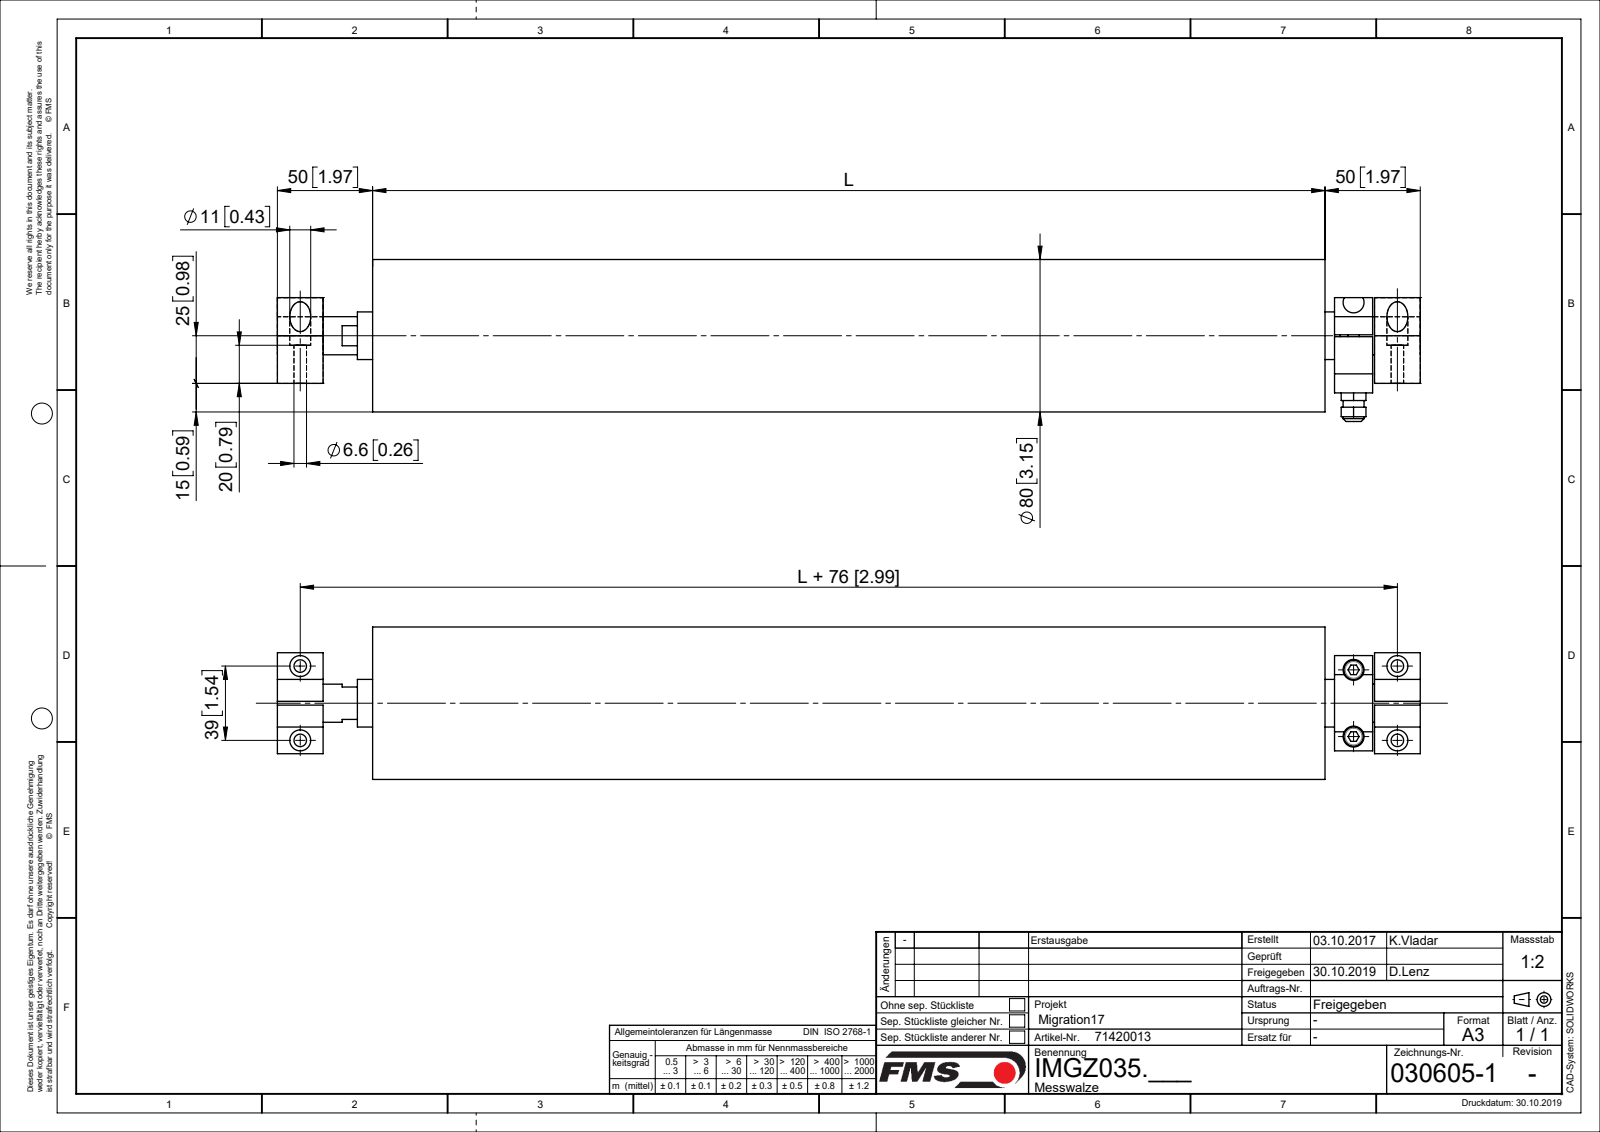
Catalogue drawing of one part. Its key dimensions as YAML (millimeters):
part_name: "I0306051_800; I0306052; PENDELKUGELLAGER_1207; I0306053 (+8 more)"
step_written_by: "Mechanical Desktop 2007 (CONFIG_CONTROL_DESIGN)"
units: millimeters
bodies: {solids: 23, faces: 548, planar: 218, cylindrical: 230, other: 100}
overall_size: [900, 86, 80]
volume: 2535000
surface_area: 606645
round_holes:
  - {diameter: 11, count: 6}
  - {diameter: 6.4, count: 4}
  - {diameter: 6.6, count: 4}
  - {diameter: 5, count: 2}
  - {diameter: 5.15, count: 2}
  - {diameter: 7, count: 2}
  - {diameter: 8, count: 2}
  - {diameter: 6, count: 1}
  - {diameter: 10.44, count: 1}
  - {diameter: 10.68, count: 1}
  - {diameter: 13, count: 1}
  - {diameter: 24.5, count: 1}
round_bosses_or_shafts:
  - {diameter: 10, count: 2}
  - {diameter: 6, count: 2}
  - {diameter: 80, count: 1}
  - {diameter: 54, count: 1}
  - {diameter: 49, count: 1}
  - {diameter: 46.8, count: 1}
  - {diameter: 40, count: 1}
  - {diameter: 35, count: 1}
partial_cylinders:
  - {radius: 3.5, count: 2}
face_to_face_distances: [24, 698, 2.5, 760, 17, 777, 7, 8, 753, 94]
hole_center_spacings: [10.44, 21.47, 42.2, 17.5, 20, 22, 23.09, 30.15]
